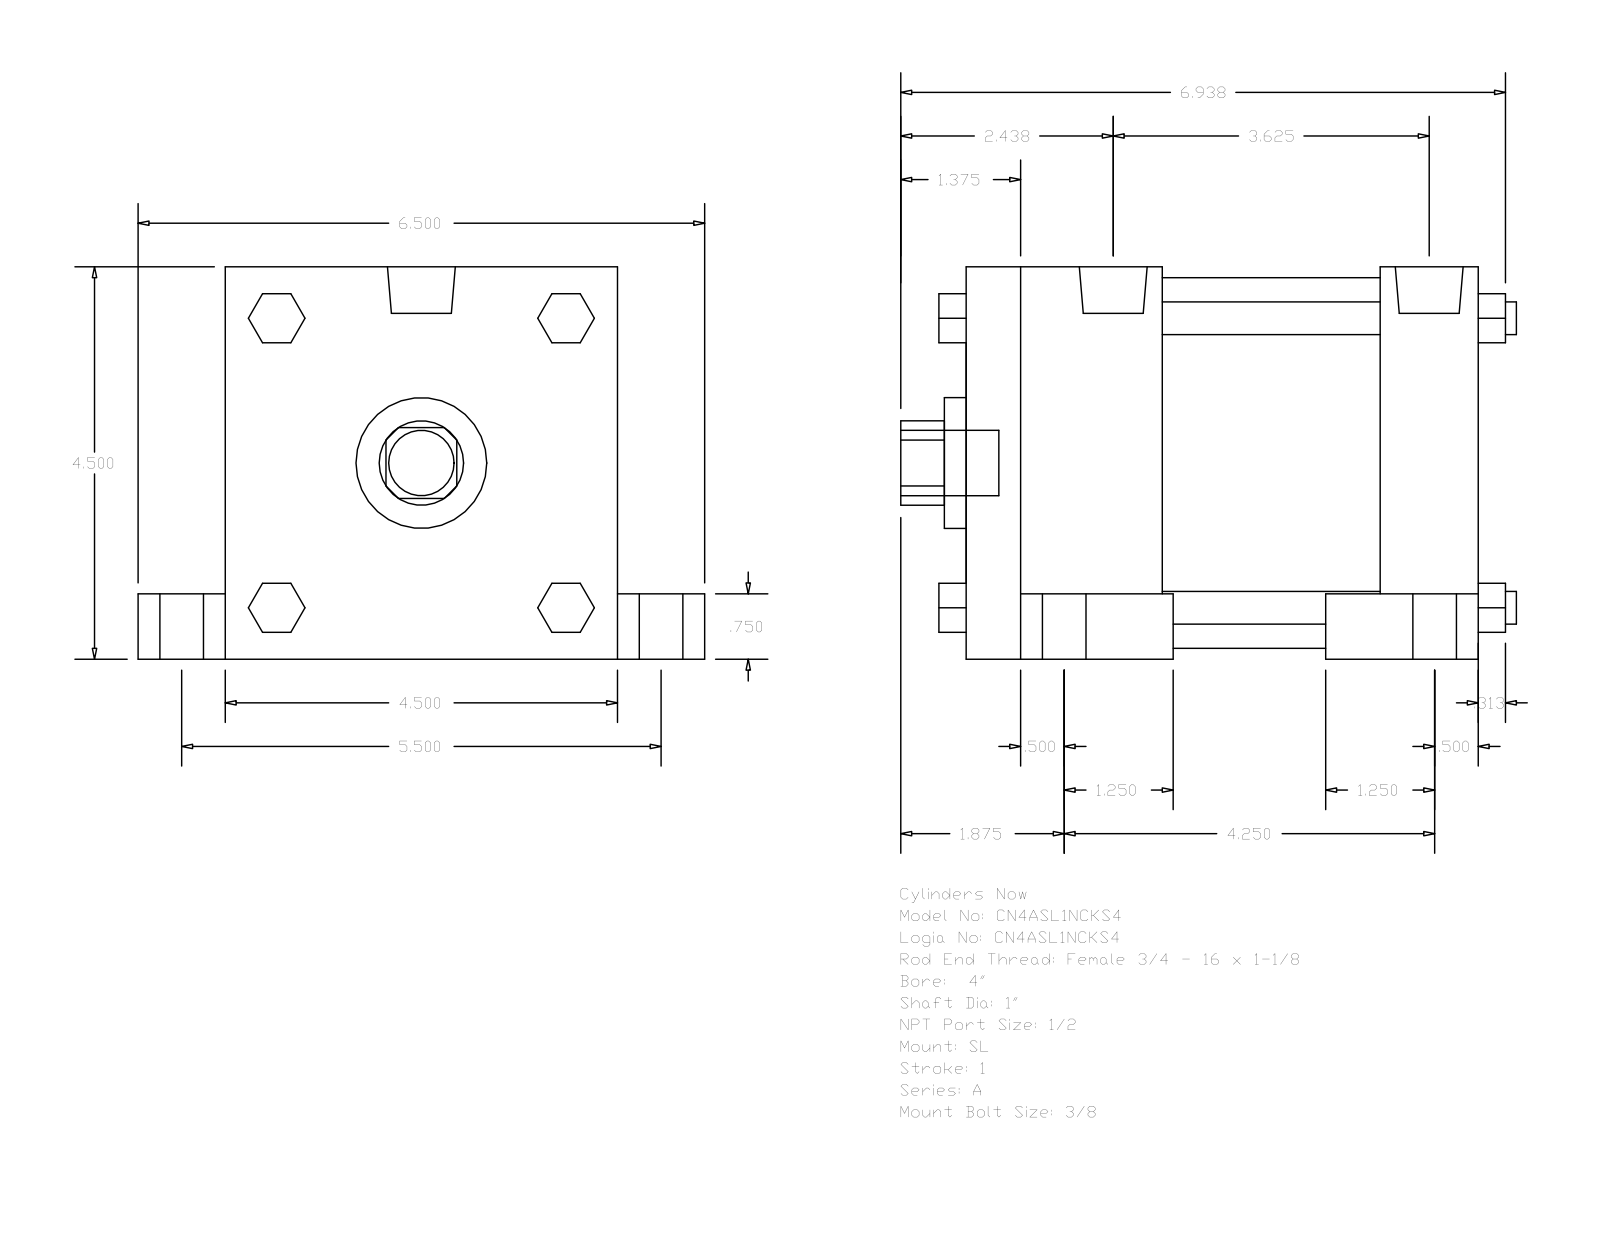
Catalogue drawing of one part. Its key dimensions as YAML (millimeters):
part_name: "A_SL__0400_1"
step_written_by: "GSSL Pune (CONFIG_CONTROL_DESIGN)"
units: millimeters
bodies: {solids: 0, faces: 150, planar: 114, cylindrical: 36, other: 0}
overall_size: [179.39, 165.1, 114.3]
round_holes:
  - {diameter: 25.4, count: 1}
  - {diameter: 38.1, count: 1}
  - {diameter: 107.95, count: 1}
round_bosses_or_shafts:
  - {diameter: 19.05, count: 5}
  - {diameter: 12.7, count: 4}
  - {diameter: 9.53, count: 4}
  - {diameter: 8.73, count: 4}
  - {diameter: 19.77, count: 2}
partial_cylinders:
  - {radius: 12.29, count: 1}
face_to_face_distances: [114.3, 149.23, 63.5, 57.15, 92.08, 120.65, 28.58, 139.7, 19.05, 25.4]
